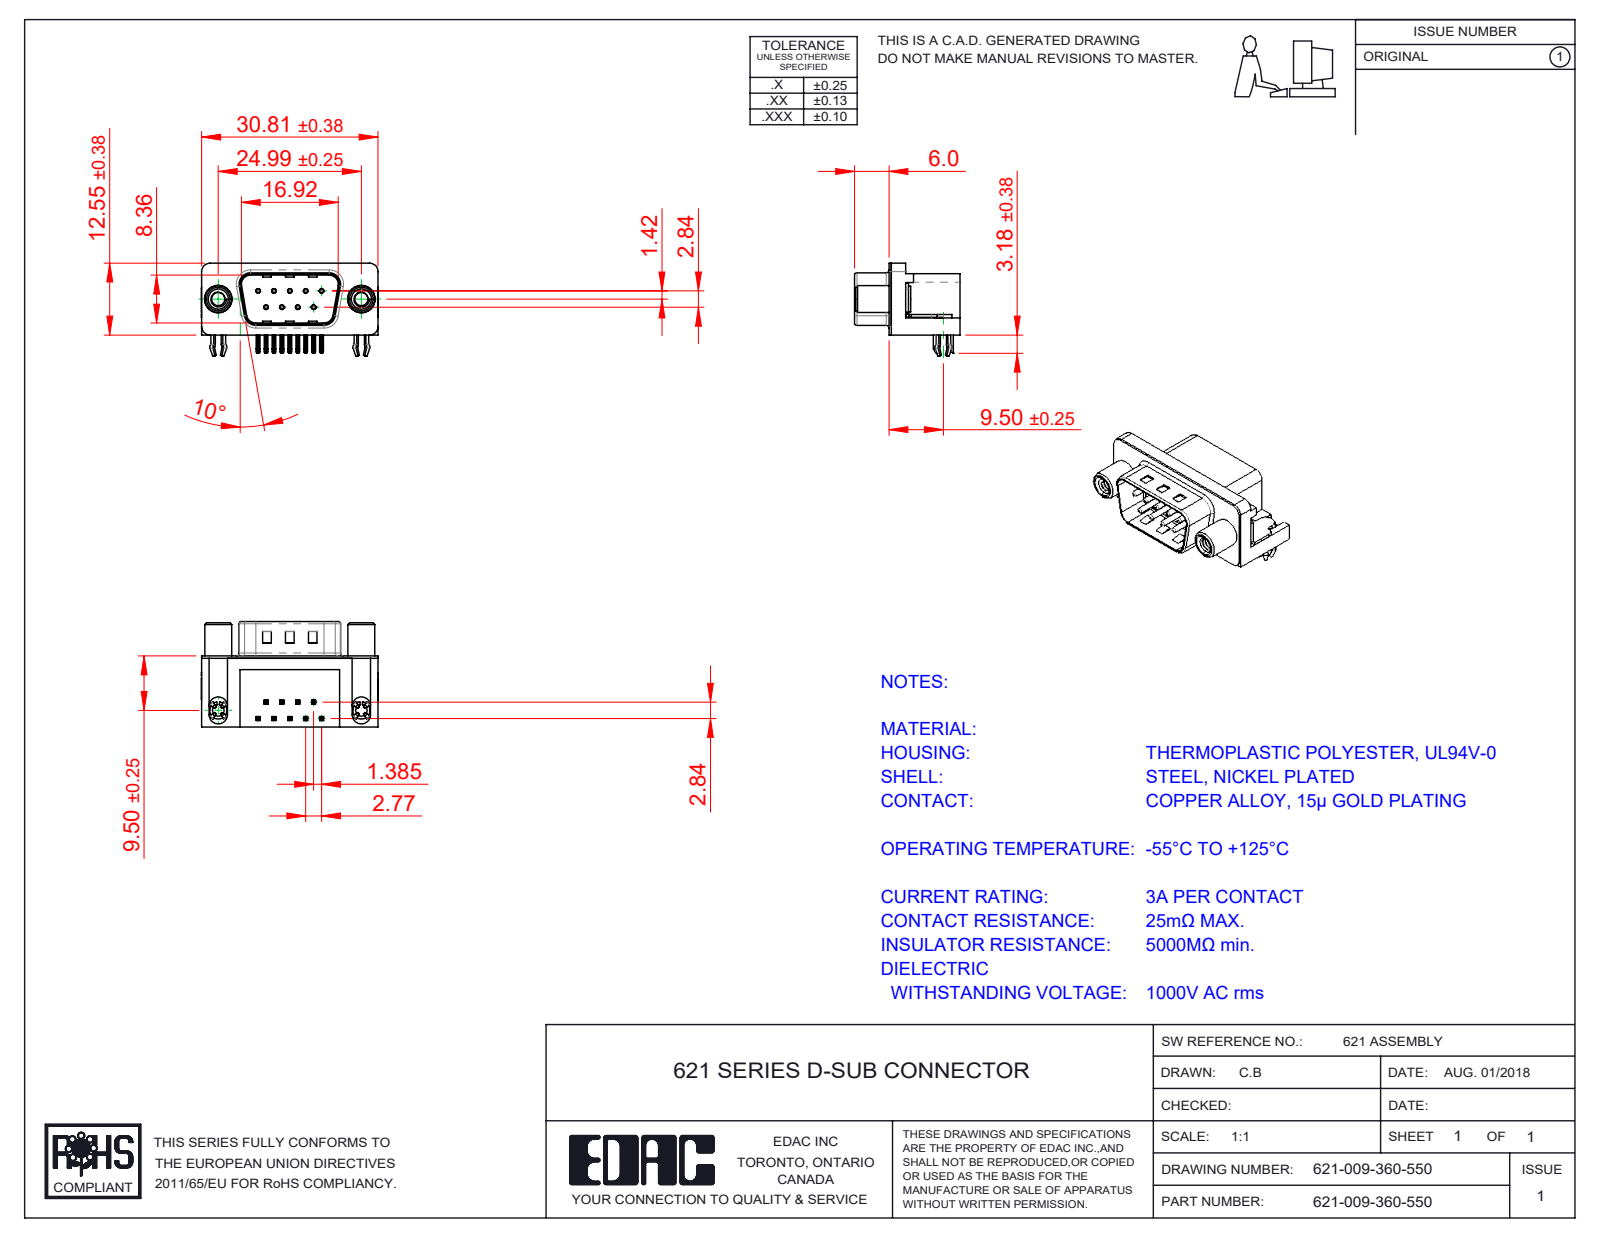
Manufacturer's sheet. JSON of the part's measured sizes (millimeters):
{"part_name": "621-009-360-550; 621 Contact Top; 621 4-40 Threaded Board Mount; 621 Round Threaded Standoff (+3 more)", "step_written_by": "SolidWorks 2016 (CONFIG_CONTROL_DESIGN)", "units": "millimeters", "bodies": {"solids": 15, "faces": 1015, "planar": 565, "cylindrical": 335, "other": 115}, "overall_size": [30.89, 18.4, 15.73], "volume_mm3": 3348, "surface_area_mm2": 4699, "round_holes": [[0.35, 9], [0.8, 9], [2.26, 2], [2.3, 2], [3.1, 2], [4, 2], [4.8, 2], [5, 2]], "round_bosses_or_shafts": [[0.75, 9], [4.9, 2], [4.7, 2], [4.5, 2], [3.85, 2], [3.26, 2]], "partial_cylinders_radius": [[0.25, 36], [0.12, 18], [1, 16], [0.5, 9], [1.5, 8], [1.6, 8], [0.9, 4], [2, 4]], "face_to_face_distances": [0.4, 12, 12.4, 10.35, 2.5, 2.9, 9.5, 2.1, 0.5, 0.35], "hole_center_spacings": [3.16, 2.77, 5.54, 5.03, 5.04, 8.31, 7.48, 7.49]}
